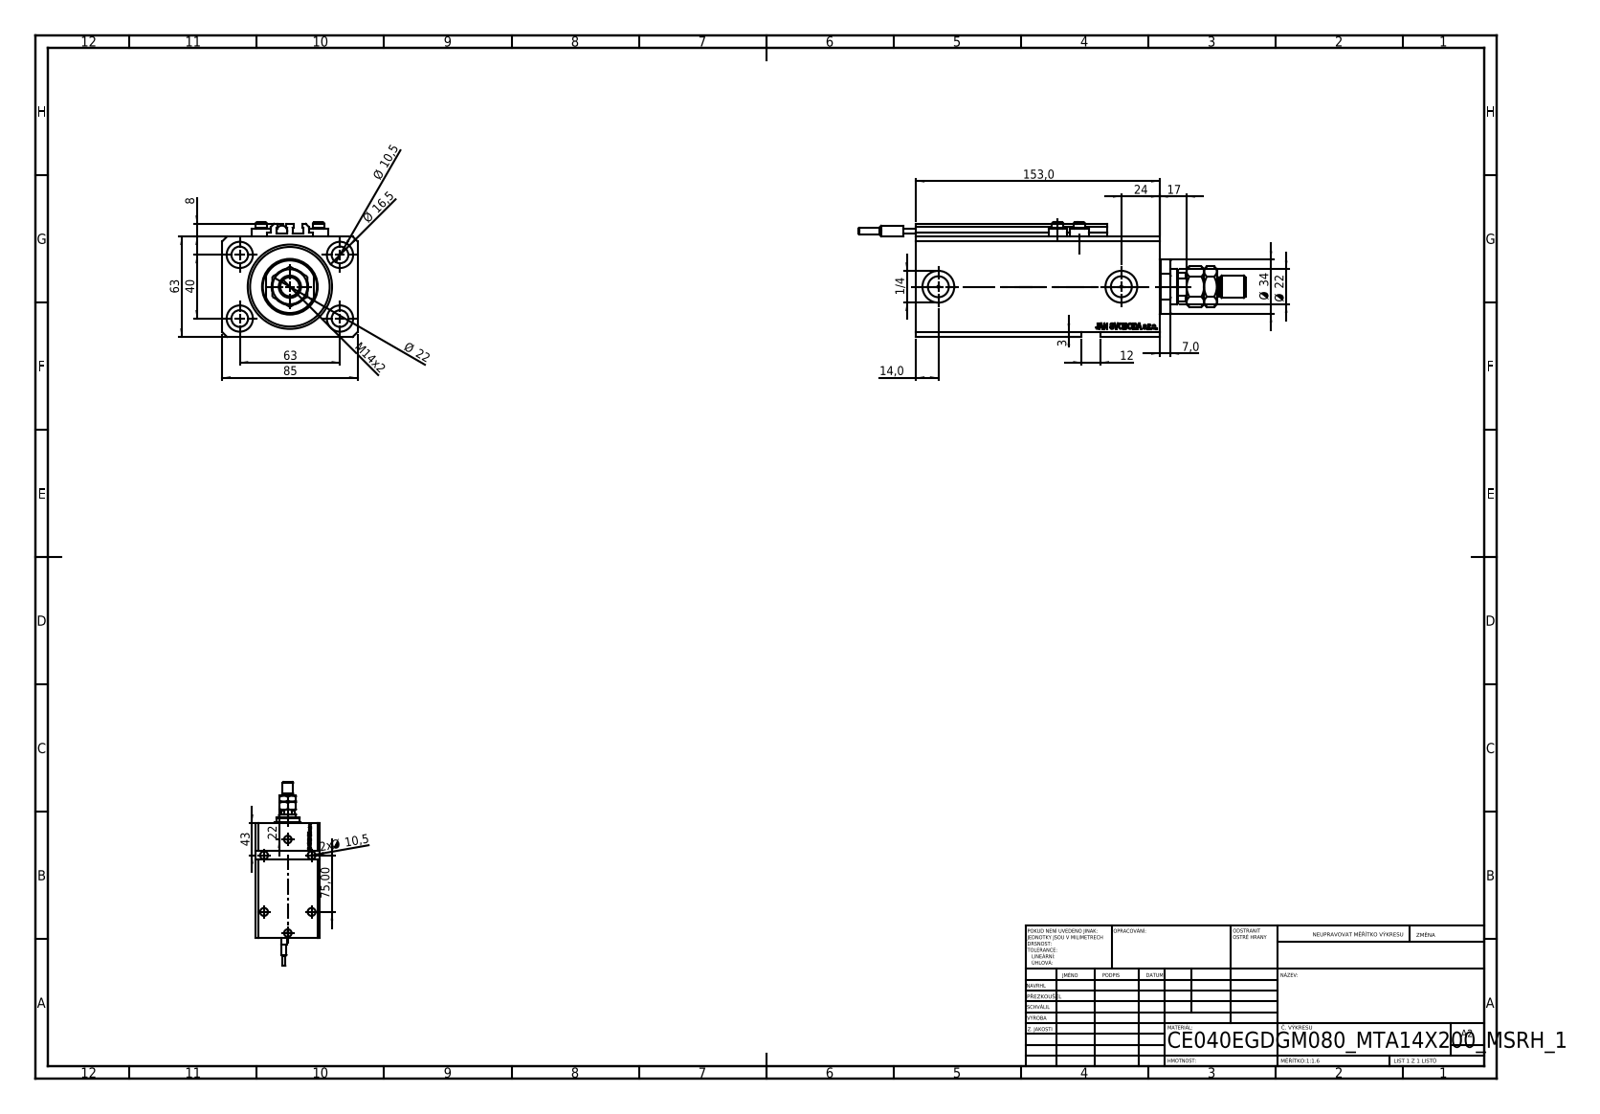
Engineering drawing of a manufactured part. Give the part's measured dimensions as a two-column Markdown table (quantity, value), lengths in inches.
| quantity | value |
| --- | --- |
| part name | SWITCH_V250CE; V250CE_C_VCP; ALLEN BOLT V250CE; MTA (+2 more) |
| STEP written by | SolidWorks 2019 (CONFIG_CONTROL_DESIGN) |
| units | inches |
| bodies | 10 solids, 1198 faces (570 planar, 168 cylindrical, 460 other) |
| overall size | 9.567 × 3.346 × 2.835 |
| volume | 42.26 in³ |
| surface area | 226.9 in² |
| round holes (diameter × count) | 0.413 × 8, 0.049 × 4, 0.157 × 4, 0.65 × 4, 0.394 × 2, 0.518 × 2, 0.787 × 2, 0.492 × 1, 0.866 × 1, 1.575 × 1, 2.087 × 1 |
| round bosses / shafts (diameter × count) | 0.457 × 4, 0.276 × 4, 1.339 × 1, 0.551 × 1, 0.472 × 1, 0.268 × 1, 0.256 × 1, 0.157 × 1 |
| partial cylindrical surfaces (radius × count) | 0.008 × 10, 0.413 × 1 |
| main face-to-face distances | 2.48, 3.346, 0.669, 6.024, 5.354, 0.449, 4.906, 5.575, 2.559, 0.118 |
| hole center spacings | 1.469, 2.48, 0.535, 0.606, 0.983, 1.324, 1.417, 1.491 |
